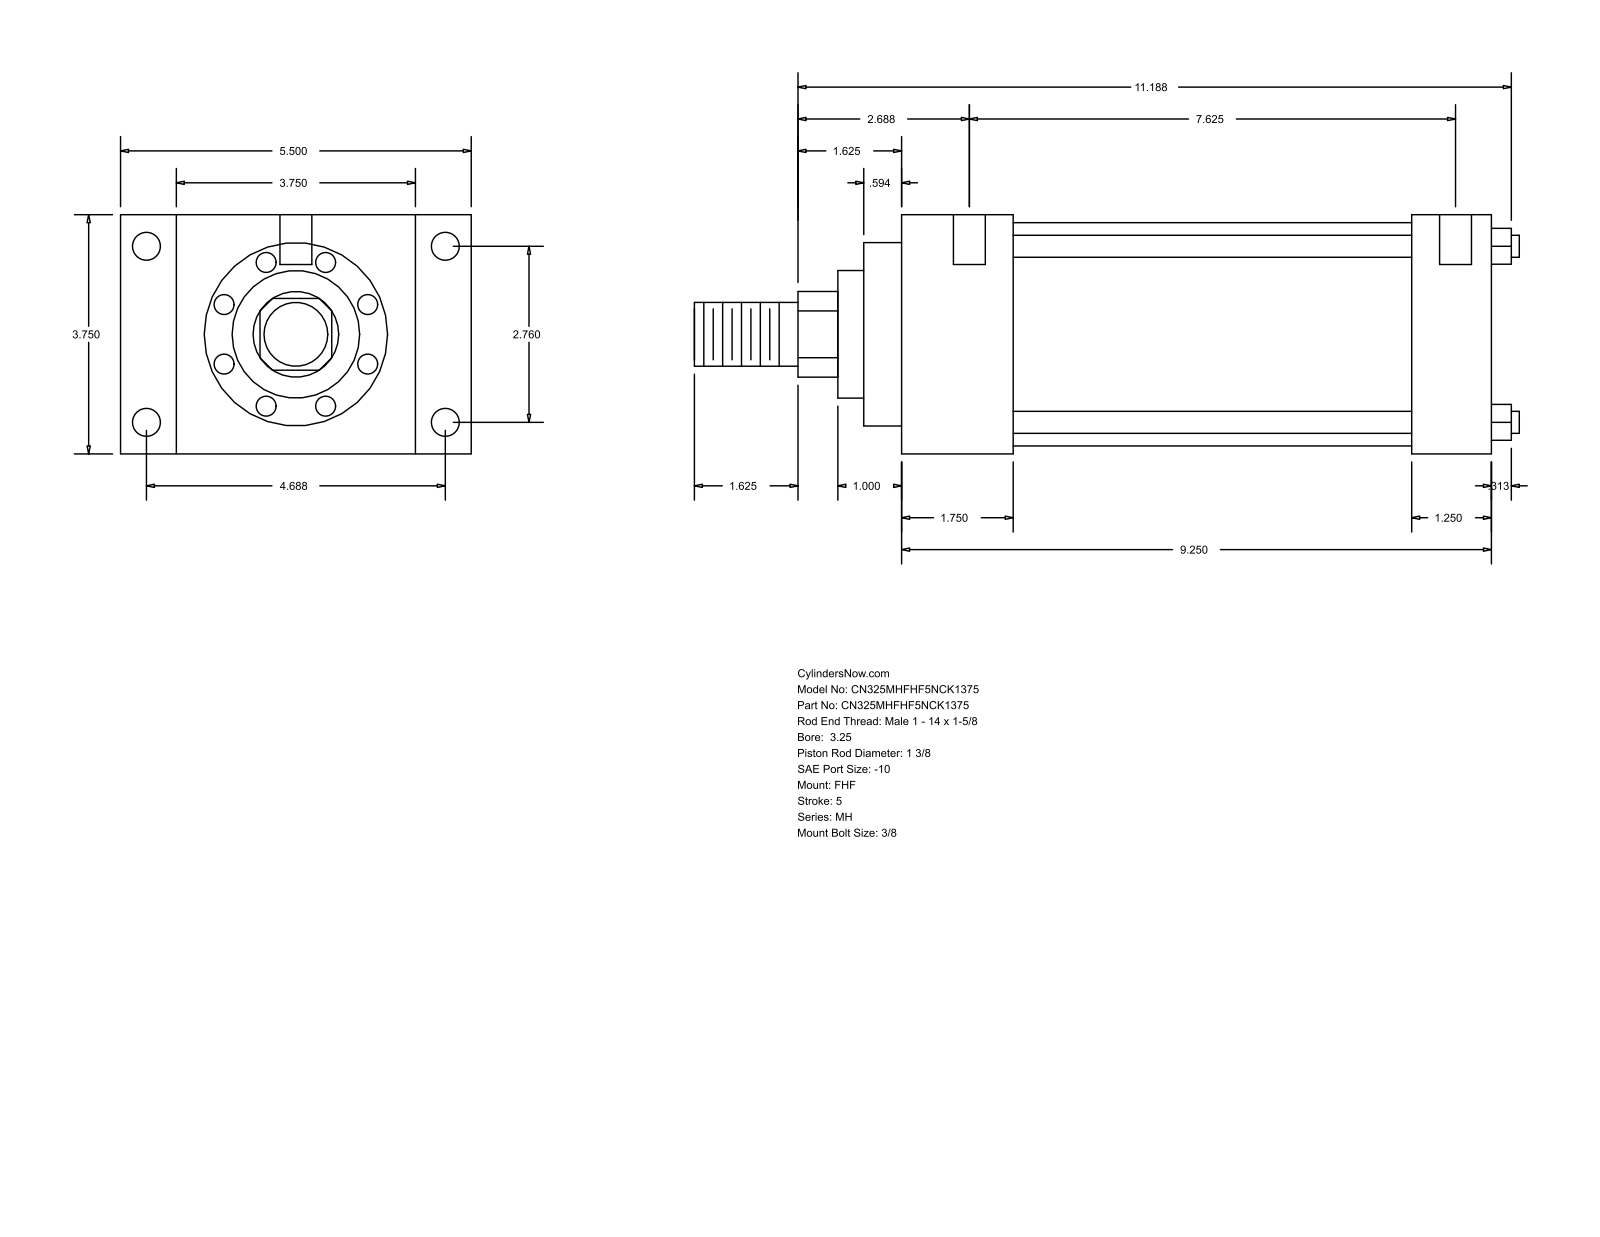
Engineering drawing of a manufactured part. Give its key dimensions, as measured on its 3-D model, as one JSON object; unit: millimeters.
{"part_name": "MH_FHF__0325_1.375", "step_written_by": "GSSL Pune (CONFIG_CONTROL_DESIGN)", "units": "millimeters", "bodies": {"solids": 0, "faces": 90, "planar": 61, "cylindrical": 29, "other": 0}, "overall_size": [328.61, 139.7, 95.25], "round_holes": [[5.56, 4], [11.13, 4], [12.7, 2]], "round_bosses_or_shafts": [[8.76, 4], [88.9, 1], [73.03, 1], [50.8, 1], [34.92, 1], [25.4, 1]], "partial_cylinders_radius": [[17.06, 1]], "face_to_face_distances": [95.24, 234.96, 44.45, 190.51, 22.23, 117.47, 139.7, 203.2, 158.75, 31.76], "hole_center_spacings": [70.1, 119.06, 138.16, 200.03, 1.59, 4.76, 193.68, 195.27]}
